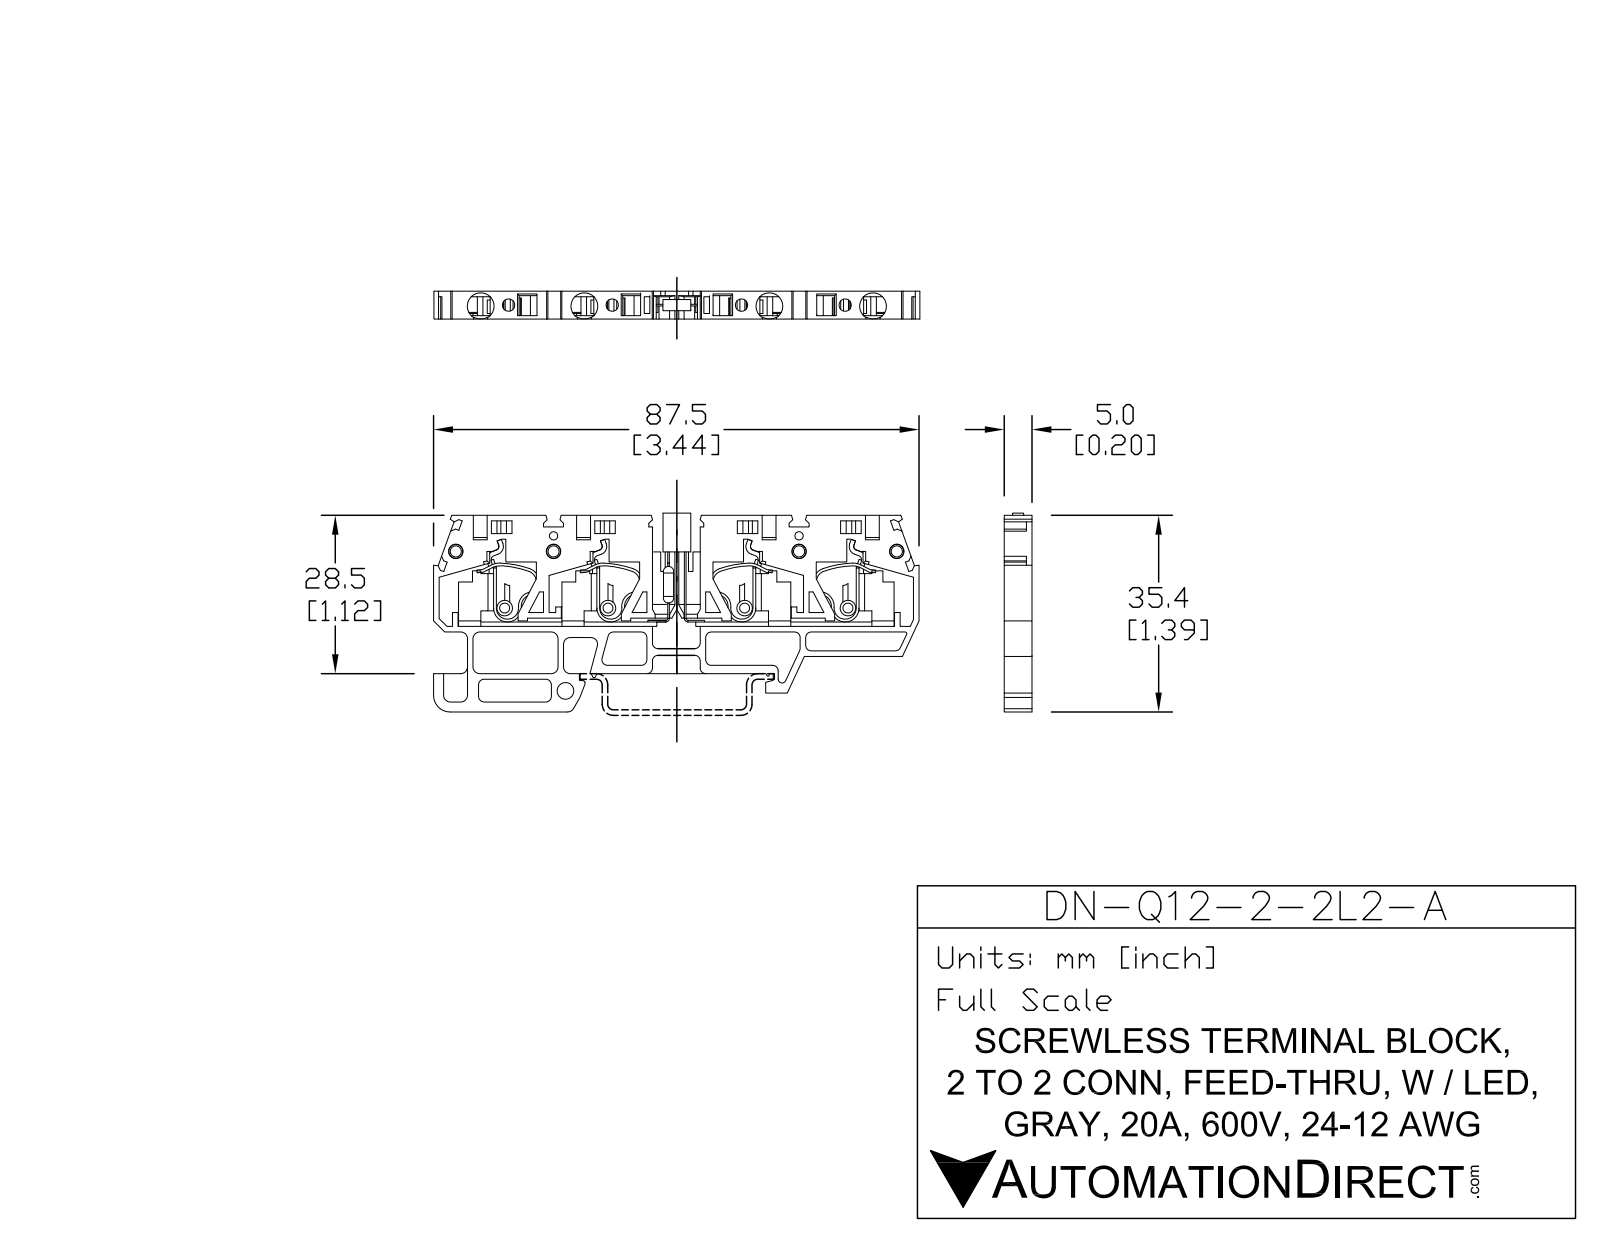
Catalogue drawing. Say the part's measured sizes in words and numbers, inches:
The part is named "42414D8_DN-Q12-2-2L2-A; 20631_Piega1 D8; 42414_DN-Q12-2-2-A; 20634 D8_20634 LN". Its 3-D file was written by "SolidWorks 2013 (AUTOMOTIVE_DESIGN)". It is 5 solids with 499 faces: 345 planar, 106 cylindrical and 48 other. Overall it measures 3.433 by 1.409 by 0.224 inches. Its volume is 0.511 cubic inches and its surface area 13.76 square inches. Round holes: 4 of diameter 0.087, 4 of diameter 0.102, 4 of diameter 0.189, 2 of diameter 0.059, 1 of diameter 0.118. Round bosses or shafts: 4 of diameter 0.012, 1 of diameter 0.071. Partial cylindrical surfaces (rounded edges, fillets, slot ends): 22 of radius 0.039, 12 of radius 0.047, 2 of radius 0.012, 1 of radius 0.028, 1 of radius 0.118. The main face-to-face distances are 0.197, 0.039, 0.079, 0.118, 0.047, 0.031, 0.331, 0.173, 0.295, 0.071. The hole center spacings are 0.197, 0.732, 1.843, 0.11, 0.535, 0.693, 0.702, 0.929.
